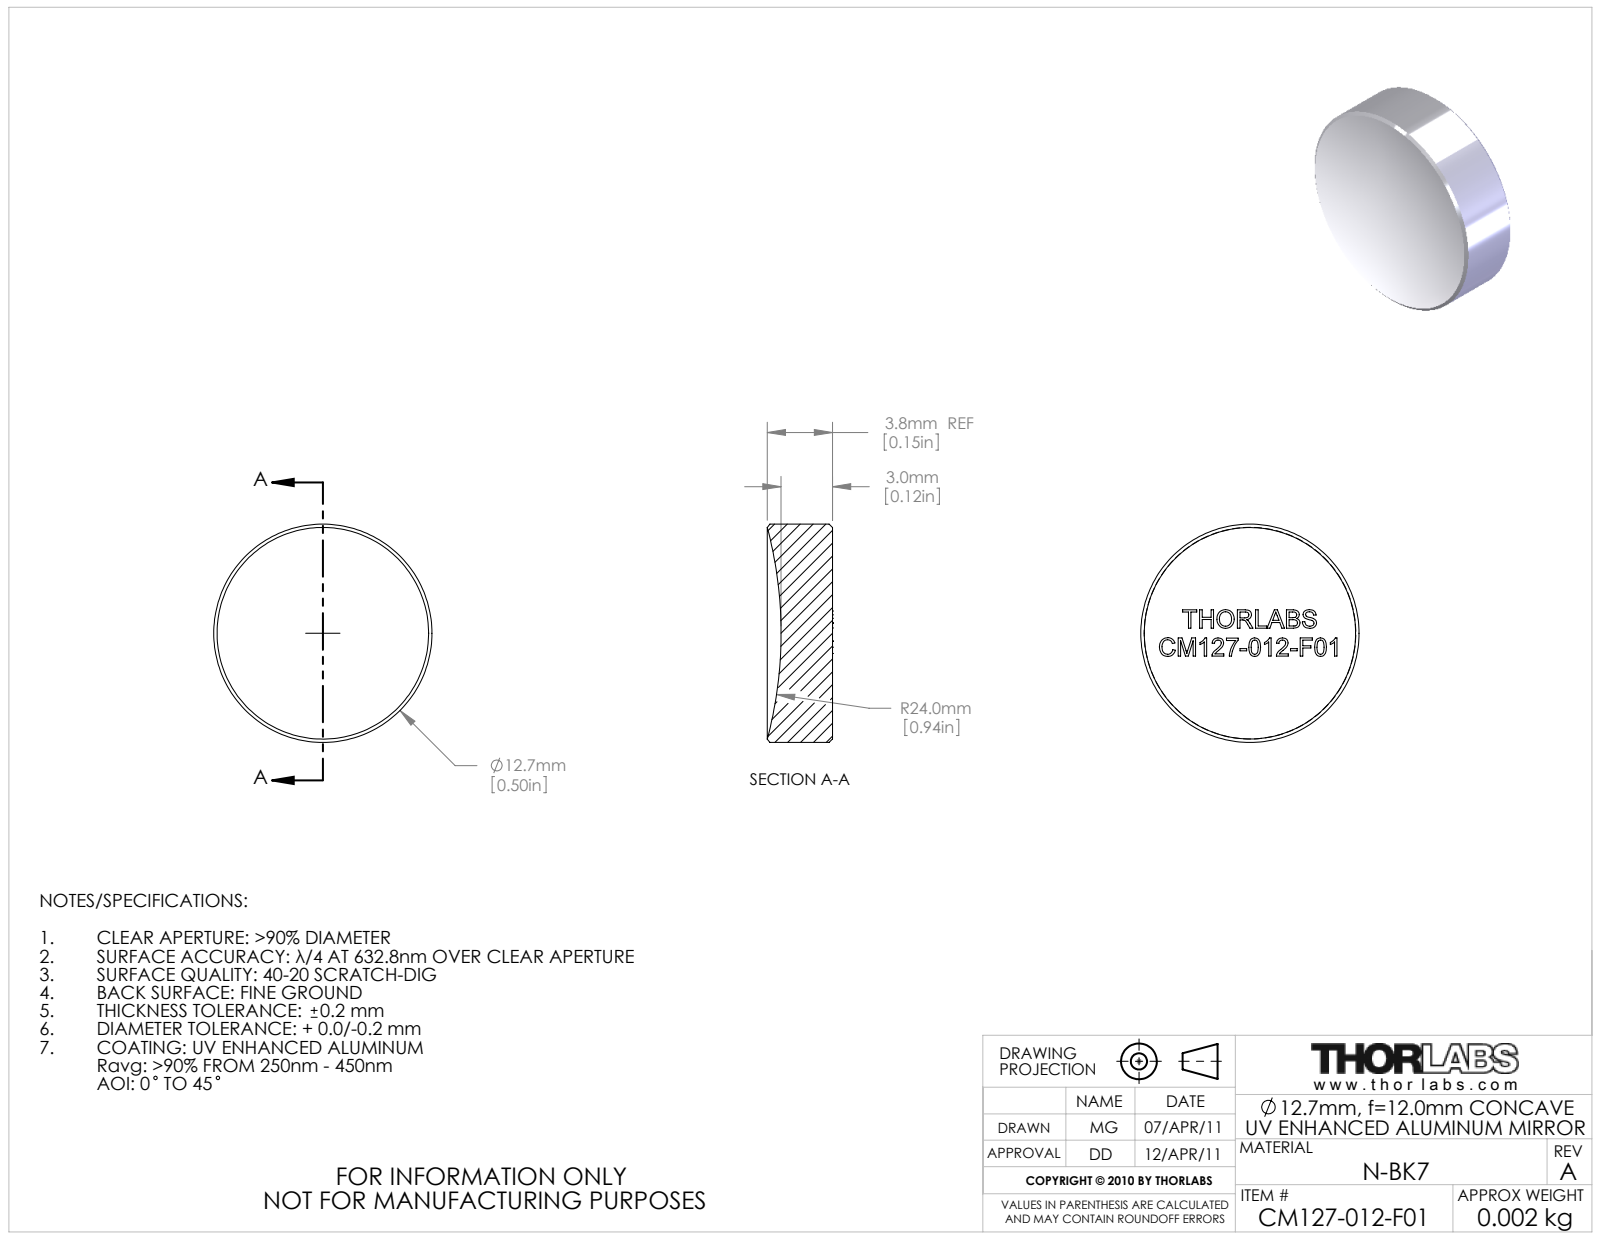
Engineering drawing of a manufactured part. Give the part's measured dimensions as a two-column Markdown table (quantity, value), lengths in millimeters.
| quantity | value |
| --- | --- |
| part name | 22191-E0W |
| STEP written by | SolidWorks 2011 (AUTOMOTIVE_DESIGN) |
| units | millimeters |
| bodies | 1 solid, 256 faces (149 planar, 2 cylindrical, 105 other) |
| overall size | 12.7 × 12.7 × 3.8 |
| volume | 430 mm³ |
| surface area | 399 mm² |
| round bosses / shafts (diameter × count) | 12.7 × 1 |
| main face-to-face distances | 1.1, 1.6, 1.3, 0.9, 0.9, 0.6, 1, 2.8, 1.5, 0.7 |
